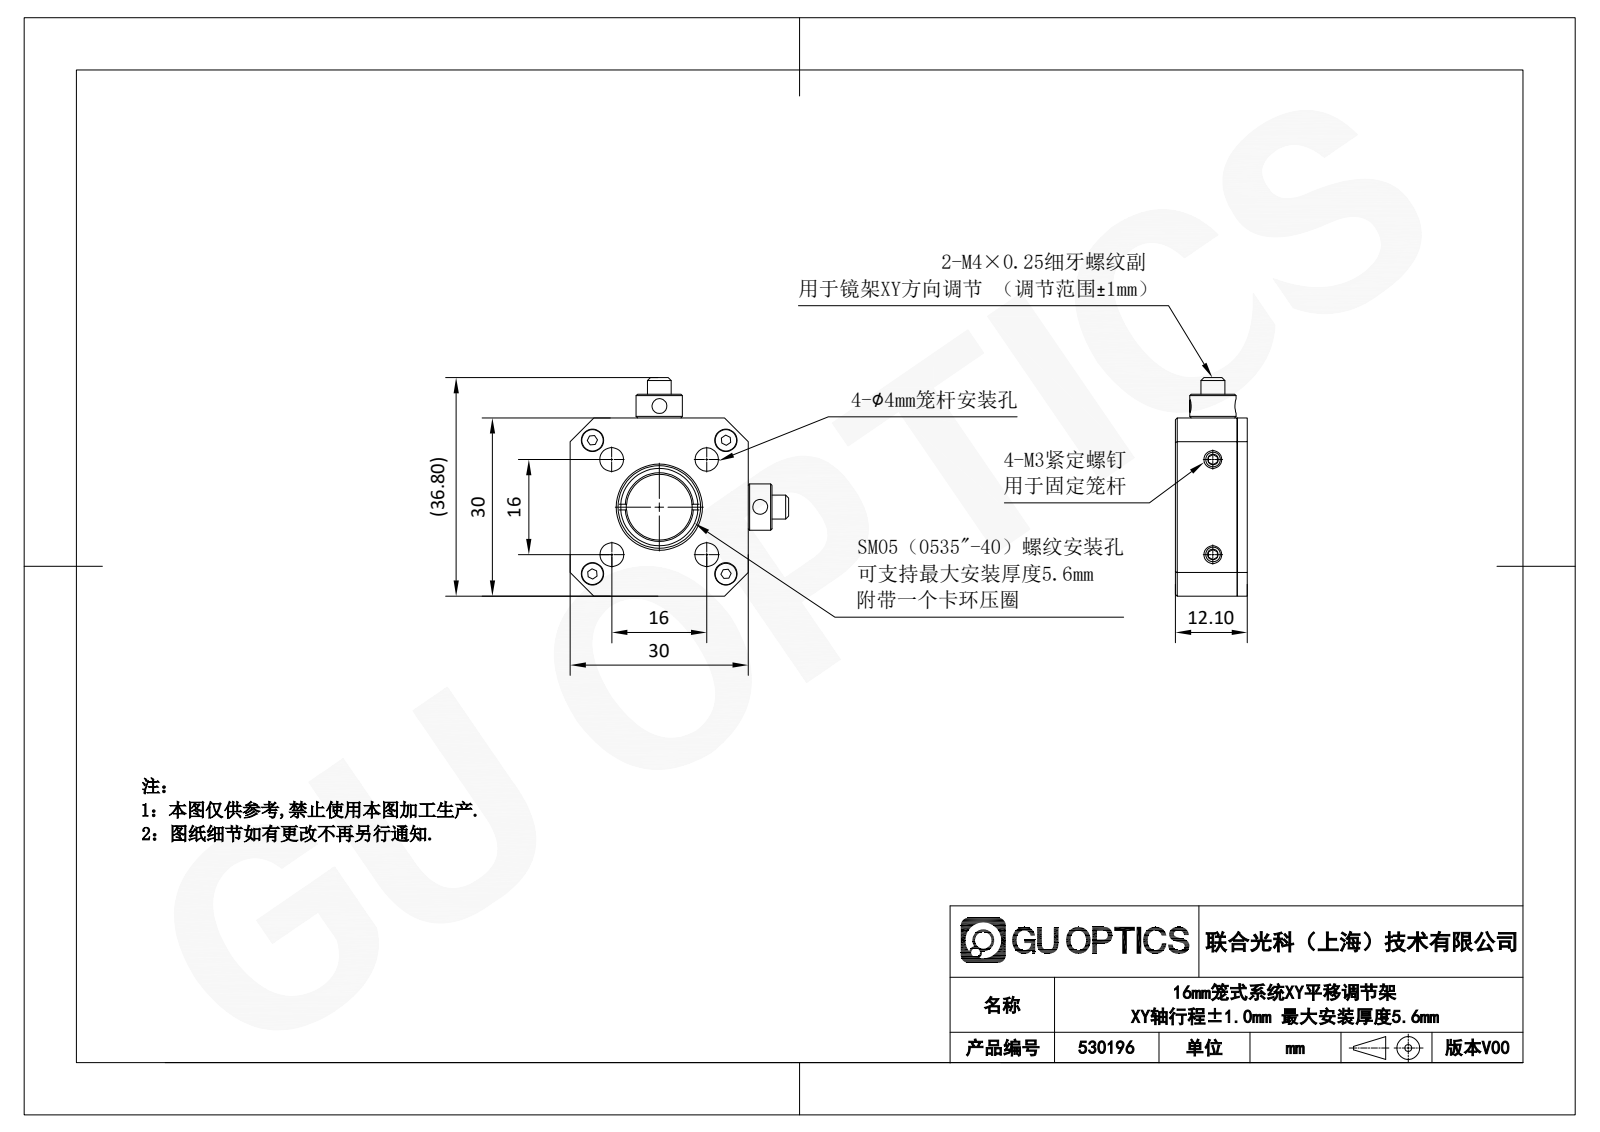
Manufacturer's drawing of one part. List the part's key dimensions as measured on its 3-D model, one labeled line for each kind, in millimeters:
Part name (STEP PRODUCT): 530196
STEP written by: SolidWorks 2020 (CONFIG_CONTROL_DESIGN)
Units: millimetres
Bodies: 18 solids, 335 faces (174 planar, 89 cylindrical, 72 other)
Overall size (bounding box): 35.92 × 35.67 × 12.1
Volume: 7 544 mm³ · Surface area: 8 349 mm²
Round holes (diameter × count): ⌀1.6 ×4, ⌀2.2 ×4, ⌀2.5 ×4, ⌀4 ×4, ⌀2.99 ×2, ⌀3.75 ×2, ⌀4.1 ×2, ⌀5.5 ×2, ⌀11.09 ×1, ⌀11.4 ×1, ⌀12.95 ×1, ⌀12.95 ×1
Round bosses / shafts (diameter × count): ⌀2 ×6, ⌀3.66 ×4, ⌀7.8 ×2, ⌀6 ×2, ⌀4 ×2, ⌀3 ×2, ⌀1.4 ×2, ⌀13.59 ×1
Partial cylindrical surfaces — rounded edges, fillets, slot ends (radius × count): R1.5 ×12, R0.8 ×4, R3.5 ×4, R10.95 ×1
Main face-to-face distances: 1.7, 10.4, 12.1, 30, 2.2, 8.2, 9.9, 36.76, 2.8, 4
Hole centre spacings: 19.52, 16, 4.6, 11.31, 15.91, 22.5, 27.22, 8
